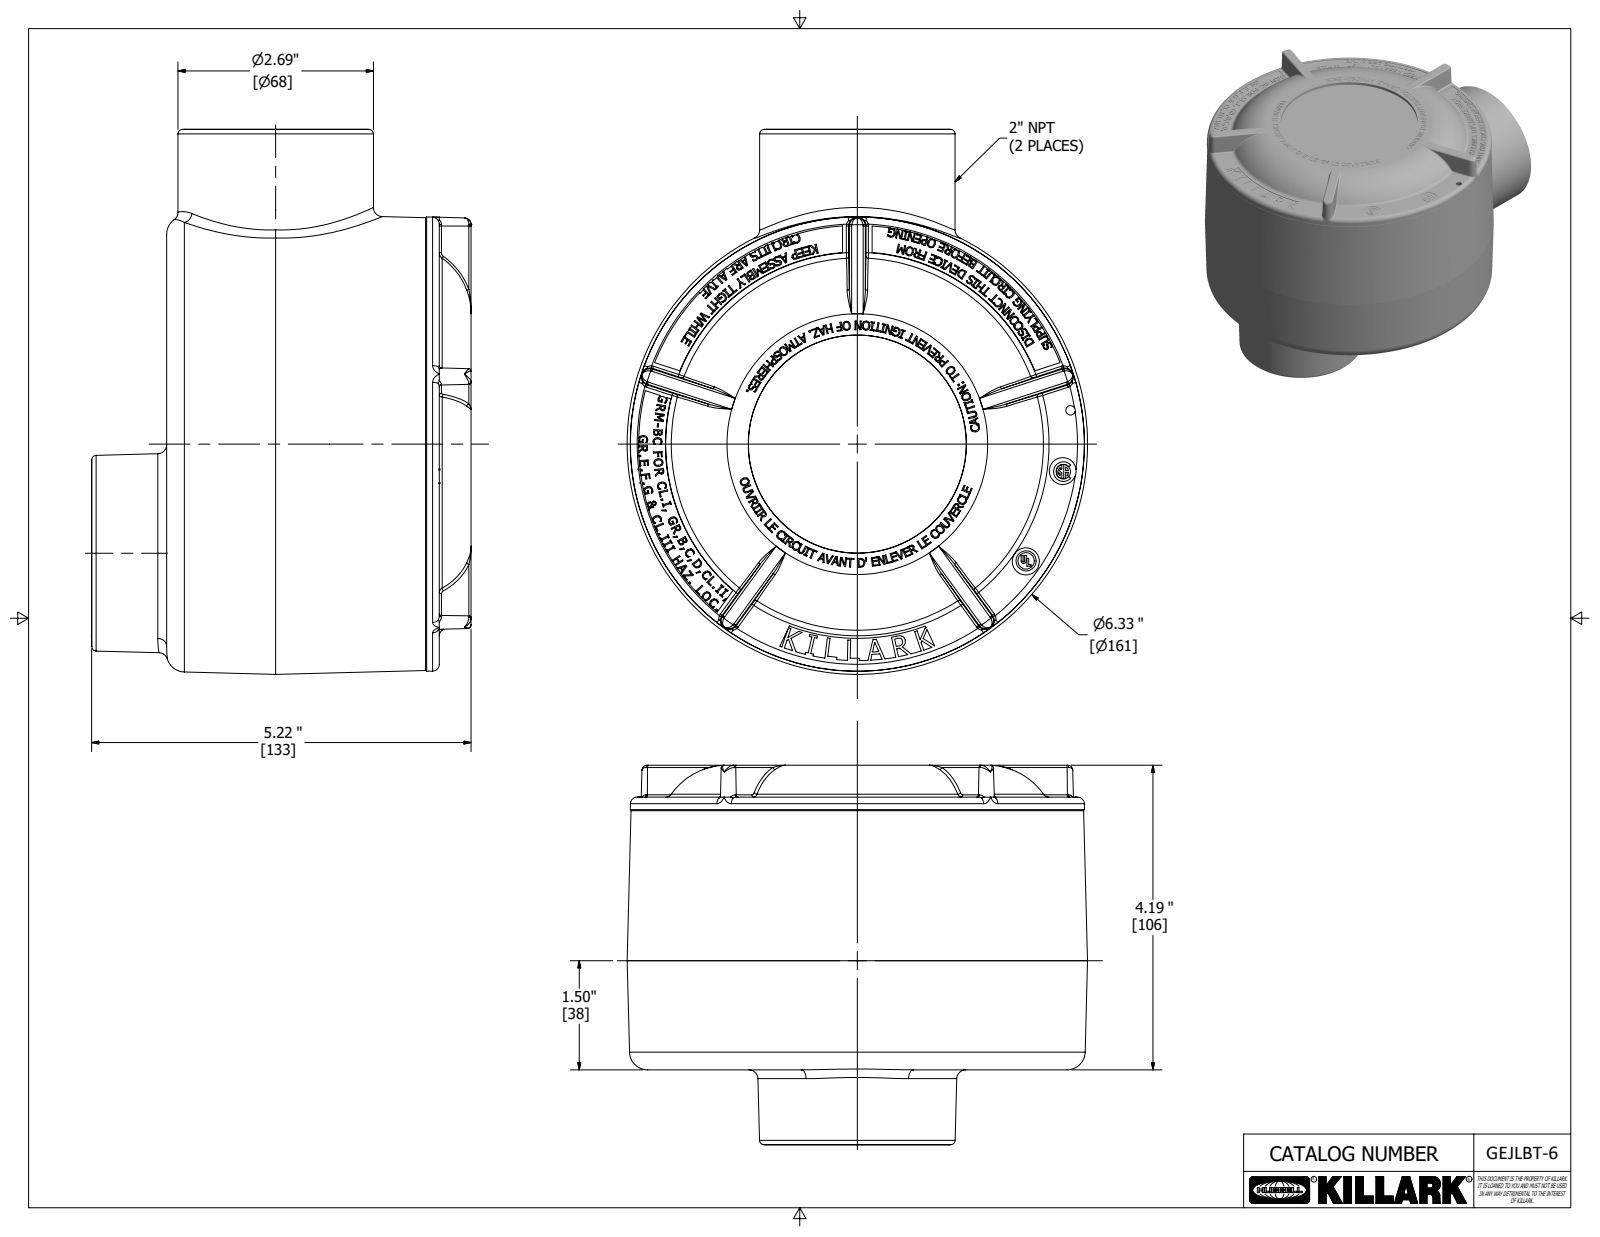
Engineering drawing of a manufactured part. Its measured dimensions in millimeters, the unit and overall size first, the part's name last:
Units: millimetres
Overall size (bounding box): 190.4 × 160.9 × 132.6
Round holes (diameter × count): ⌀50.9 ×2, ⌀3.3 ×1, ⌀5 ×1, ⌀5.7 ×1, ⌀9.4 ×1, ⌀9.4 ×1, ⌀134.2 ×1, ⌀138 ×1, ⌀144.4 ×1, ⌀146.5 ×1
Round bosses / shafts (diameter × count): ⌀136.5 ×1, ⌀68.3 ×1, ⌀7 ×1
Partial cylindrical surfaces — rounded edges, fillets, slot ends (radius × count): R0.8 ×20, R1.6 ×8, R0.2 ×1, R0.9 ×1, R1.8 ×1, R2.5 ×1, R2.5 ×1, R3.4 ×1
Main face-to-face distances: 90.5, 5.6, 96, 104.8, 14.3, 8.7, 0.8, 95.3, 1.6, 106.3
Hole centre spacings: 21.4, 33.9, 34.1, 38.1, 44.5, 54.8, 55, 57.2
Volume: 781 500 mm³ · Surface area: 209 400 mm²
Bodies: 2 solids, 5345 faces (2730 planar, 231 cylindrical, 2384 other)
Part name (STEP PRODUCT): GEJLBT-6; 0071681M; 17805ABAM
STEP written by: Autodesk Inventor 2020 (AUTOMOTIVE_DESIGN)
